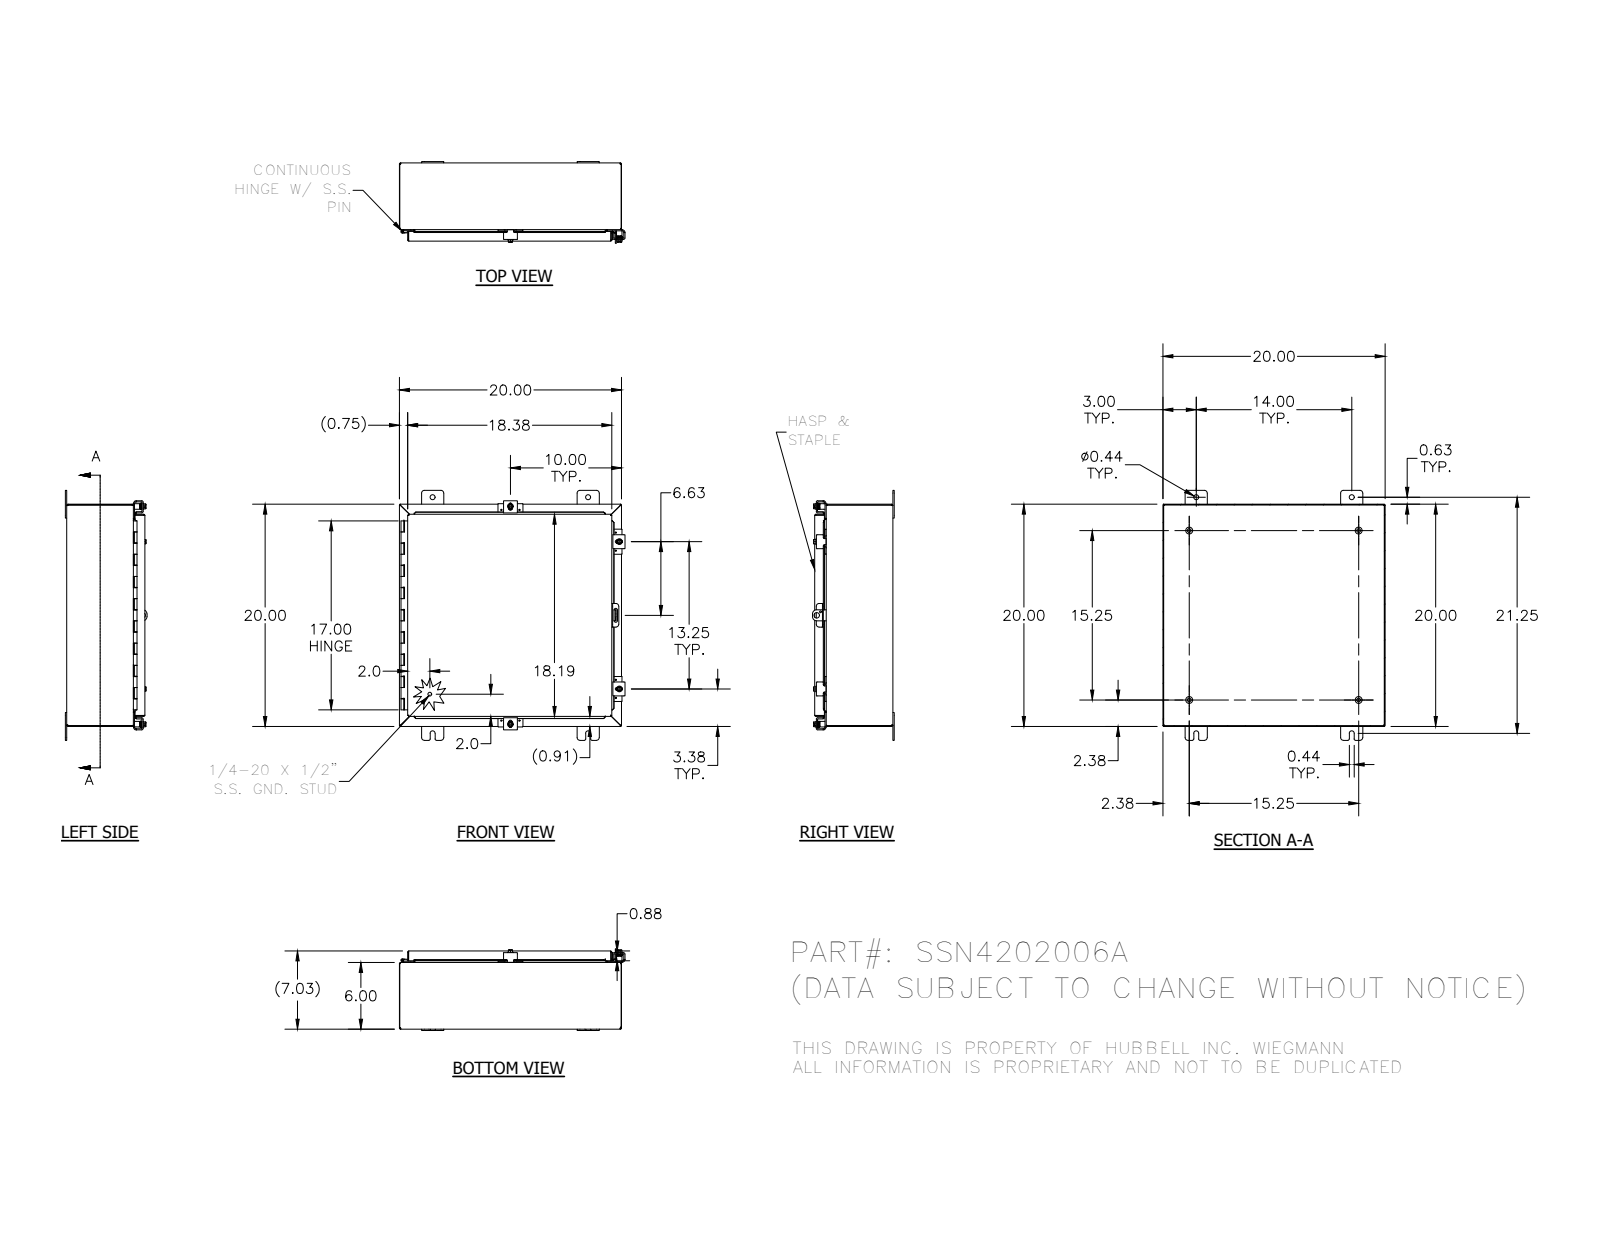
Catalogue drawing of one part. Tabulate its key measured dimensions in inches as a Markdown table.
| quantity | value |
| --- | --- |
| part name | HFW30825-4_1; 328137L_1; 32912_1; 18x18_1 (+8 more) |
| STEP written by | SolidWorks 2014 (AUTOMOTIVE_DESIGN) |
| units | inches |
| bodies | 37 solids, 1482 faces (573 planar, 644 cylindrical, 265 other) |
| overall size | 23.047 × 21.331 × 7.355 |
| volume | 121.5 in³ |
| surface area | 3 167 in² |
| round holes (diameter × count) | 0.11 × 11, 0.211 × 4, 0.281 × 4, 0.3 × 4, 0.438 × 4, 0.125 × 1, 0.156 × 1, 0.5 × 1 |
| round bosses / shafts (diameter × count) | 0.25 × 6, 0.625 × 4, 0.52 × 4, 0.5 × 4, 0.35 × 4, 0.33 × 4, 0.115 × 2, 0.337 × 1 |
| partial cylindrical surfaces (radius × count) | 0.03 × 49, 0.125 × 33, 0.25 × 29, 0.031 × 23, 0.105 × 23, 0.062 × 11, 0.07 × 8, 0.141 × 8 |
| main face-to-face distances | 0.074, 7.002, 19.926, 6.928, 7.076, 19.852, 20, 5.926, 1.076, 6 |
| hole center spacings | 0.876, 19.306, 13.25, 0.779, 0.876, 1.625, 1.625, 4.029 |
